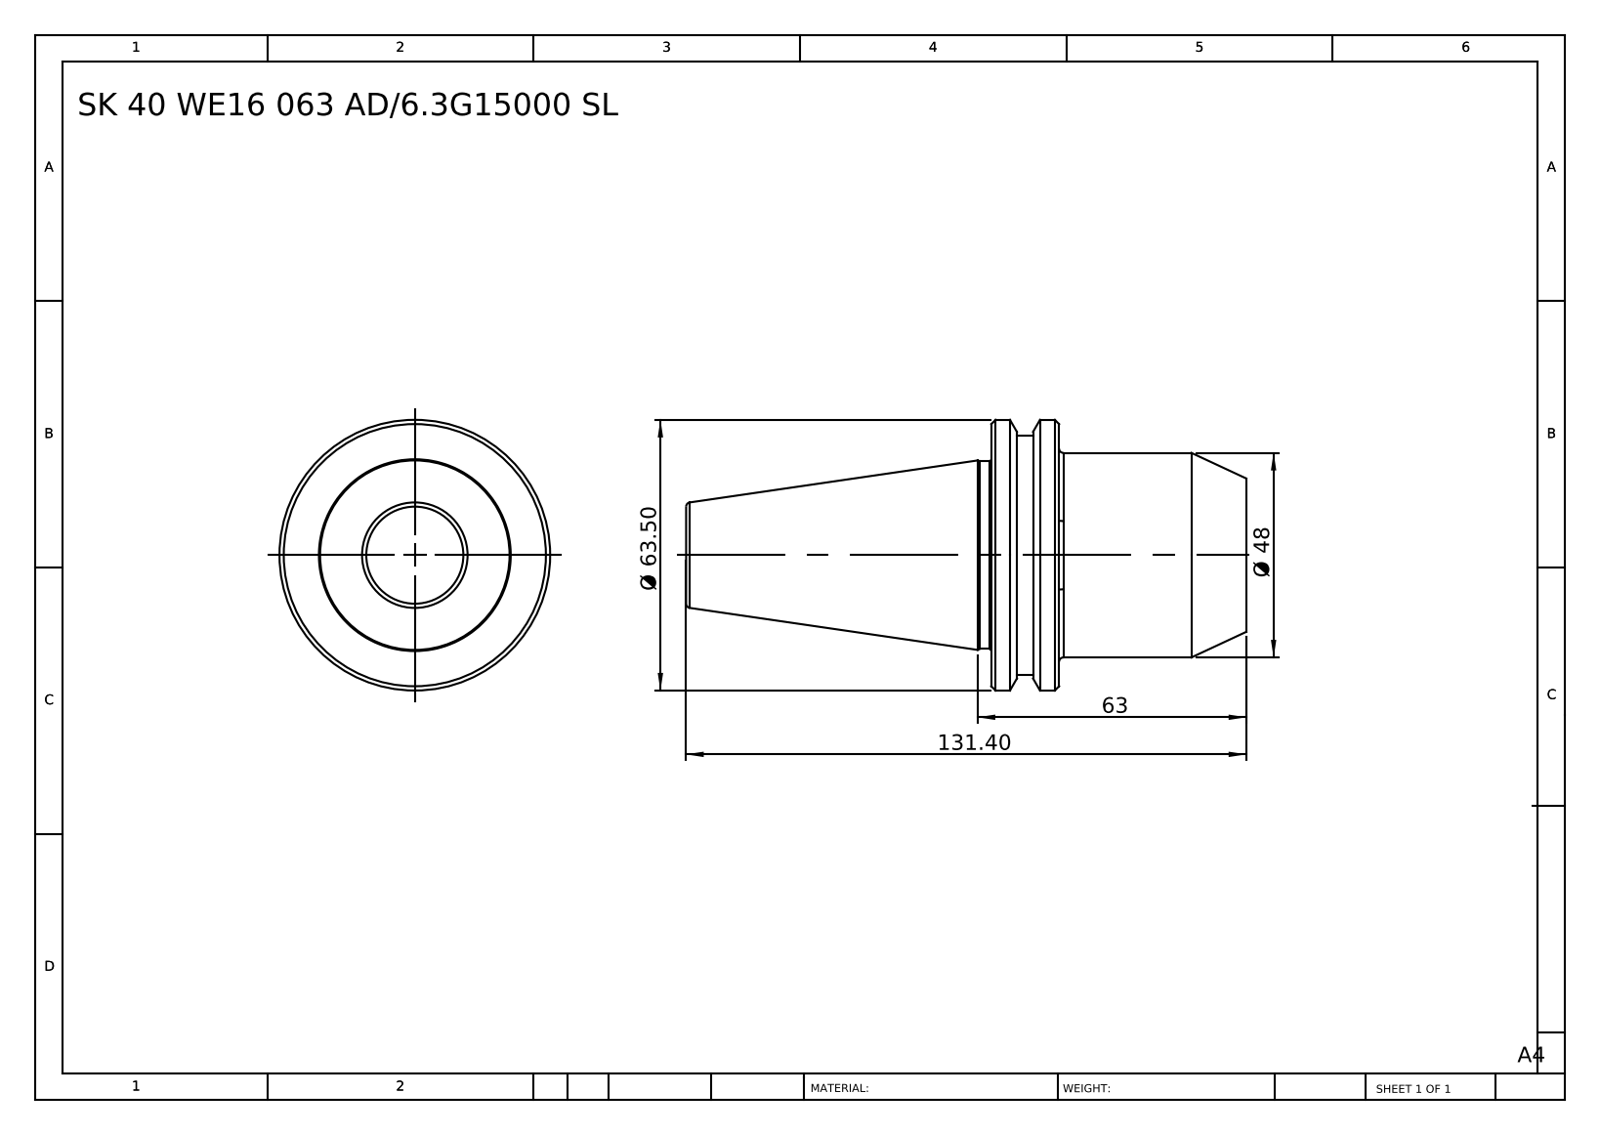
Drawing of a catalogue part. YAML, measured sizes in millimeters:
part_name: "SK40 WE16 063 AD-6.3G15000 SL"
step_written_by: "SolidWorks 2014 (CONFIG_CONTROL_DESIGN)"
units: millimeters
bodies: {solids: 1, faces: 36, planar: 6, cylindrical: 10, other: 20}
overall_size: [131.4, 63.5, 63.5]
volume: 191241
surface_area: 22639
round_bosses_or_shafts:
  - {diameter: 63.5, count: 1}
  - {diameter: 56, count: 1}
  - {diameter: 48, count: 1}
  - {diameter: 44, count: 1}
face_to_face_distances: [59.8, 43.9, 15.9, 131.4, 87.5, 71.6, 50, 6.1, 9.8, 81.4]
